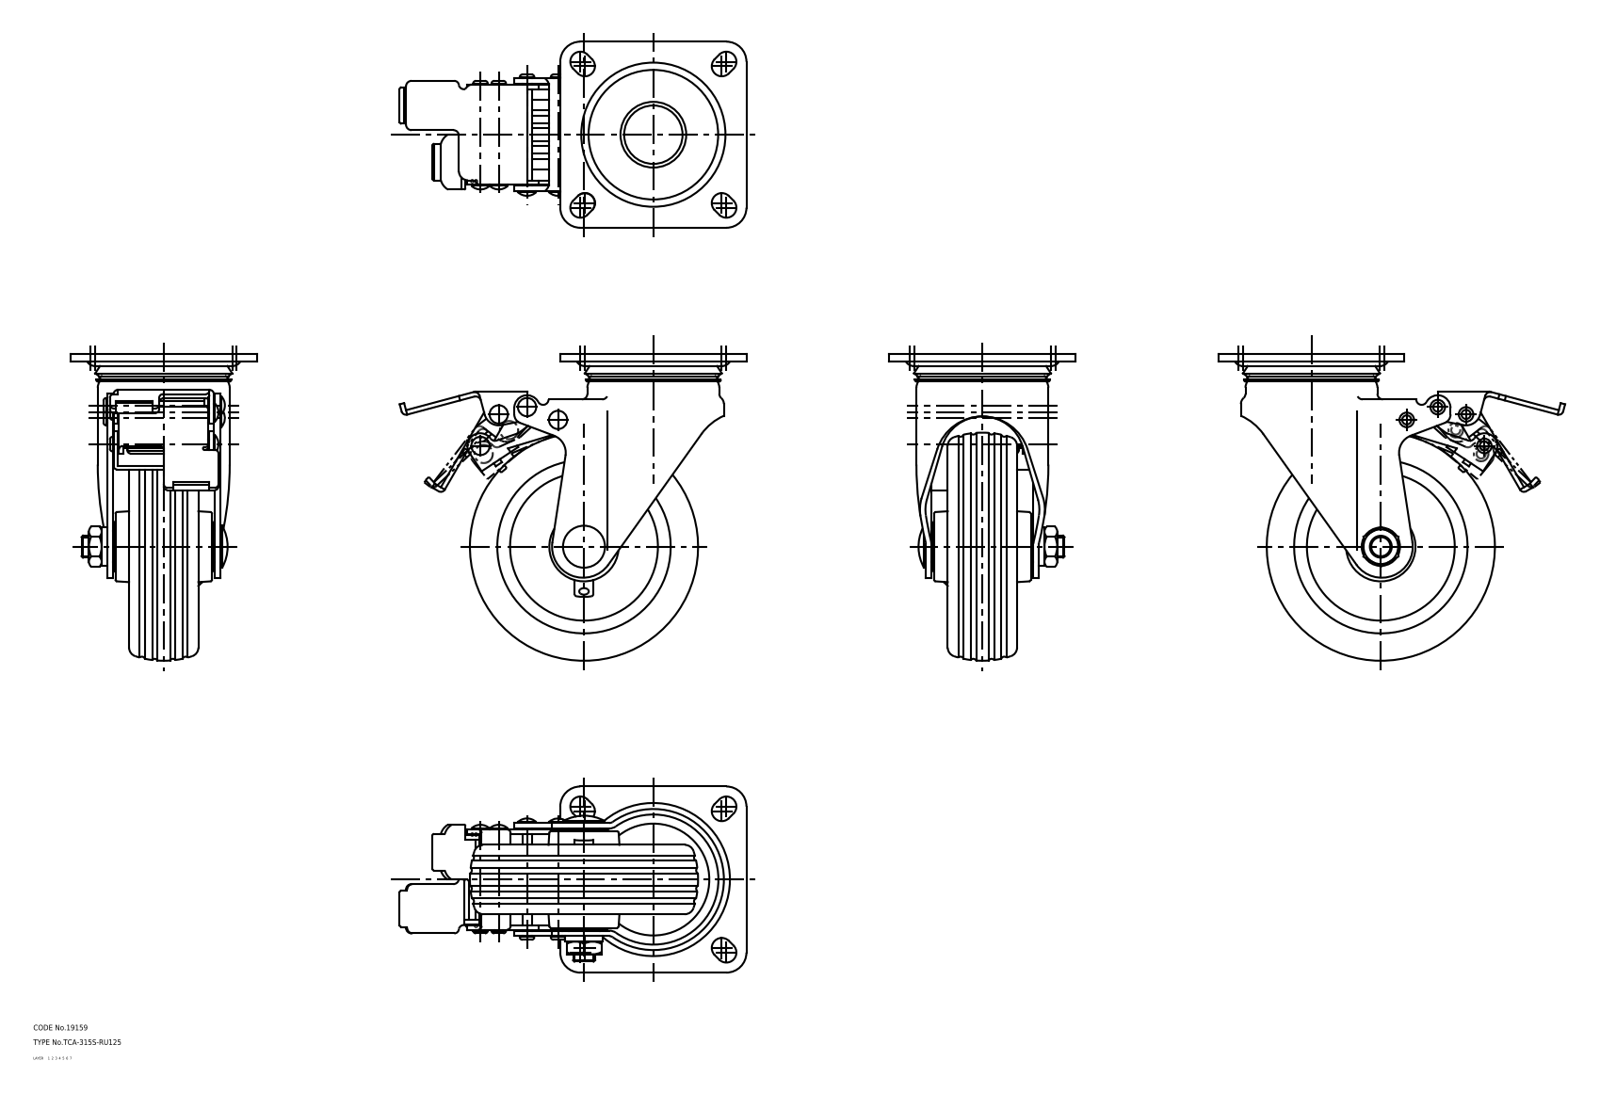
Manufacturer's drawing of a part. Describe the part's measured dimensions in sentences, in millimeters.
The part is named "67144880; 67144893; 67144906; 67144919 (+8 more)". Its 3-D file was written by "CADfix (AUTOMOTIVE_DESIGN)". It is 5 solids with 493 faces: 0 planar, 0 cylindrical and 493 other. Overall it measures 189.97 by 168 by 102 millimeters. Its volume is 556 067 cubic millimeters and its surface area 148 619 square millimeters.
